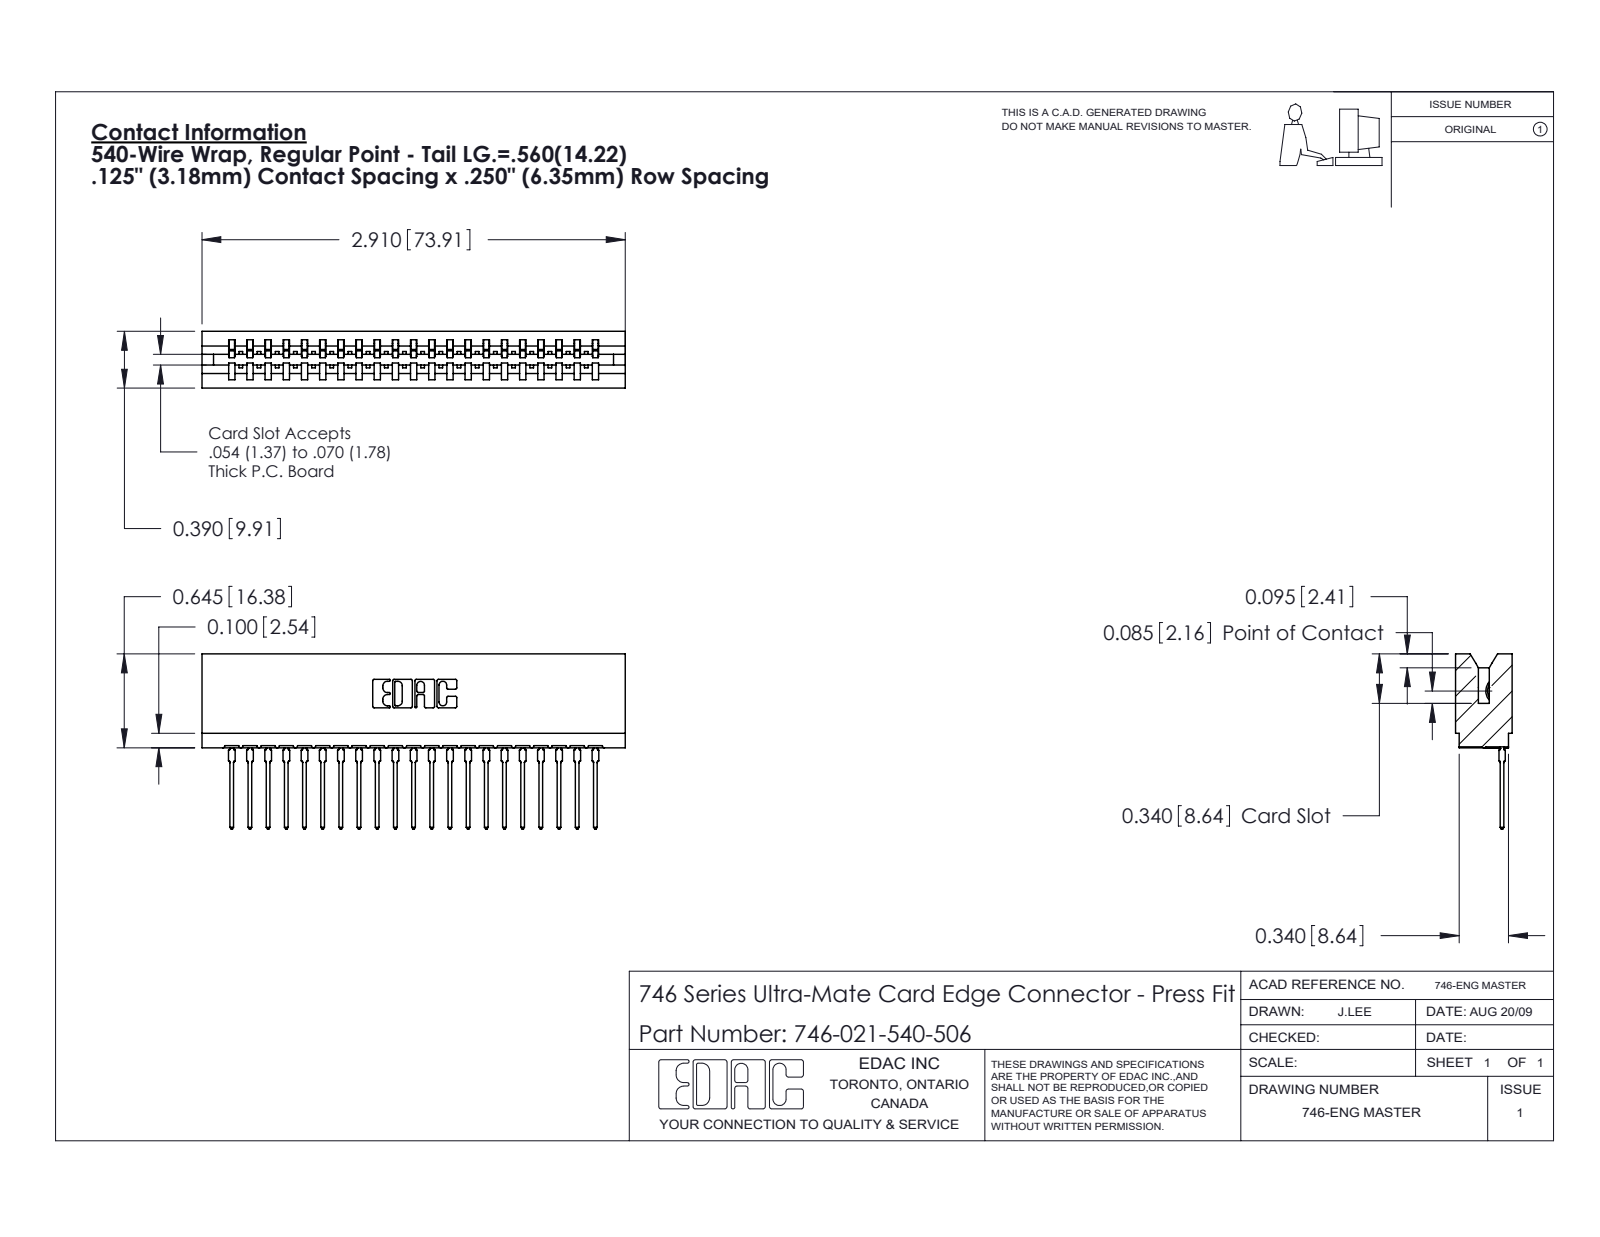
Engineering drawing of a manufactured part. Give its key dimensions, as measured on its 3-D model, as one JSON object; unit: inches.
{"part_name": "746 Part_.340 Slot Depth - 06; 746-021-540-506; 746-292-001_540", "step_written_by": "SolidWorks 2020 (CONFIG_CONTROL_DESIGN)", "units": "inches", "bodies": {"solids": 22, "faces": 2366, "planar": 1379, "cylindrical": 441, "other": 546}, "overall_size": [2.91, 1.204, 0.39], "volume_in3": 0.516, "surface_area_in2": 17.59, "partial_cylinders_radius": [[0.021, 42], [0.01, 22], [0.015, 22], [0.007, 6], [0.031, 6], [0.005, 4], [0.011, 4], [0.026, 3]], "face_to_face_distances": [0.333, 0.25, 0.057, 0.39, 0.5, 0.025, 0.307, 0.083, 0.042, 0.125]}
